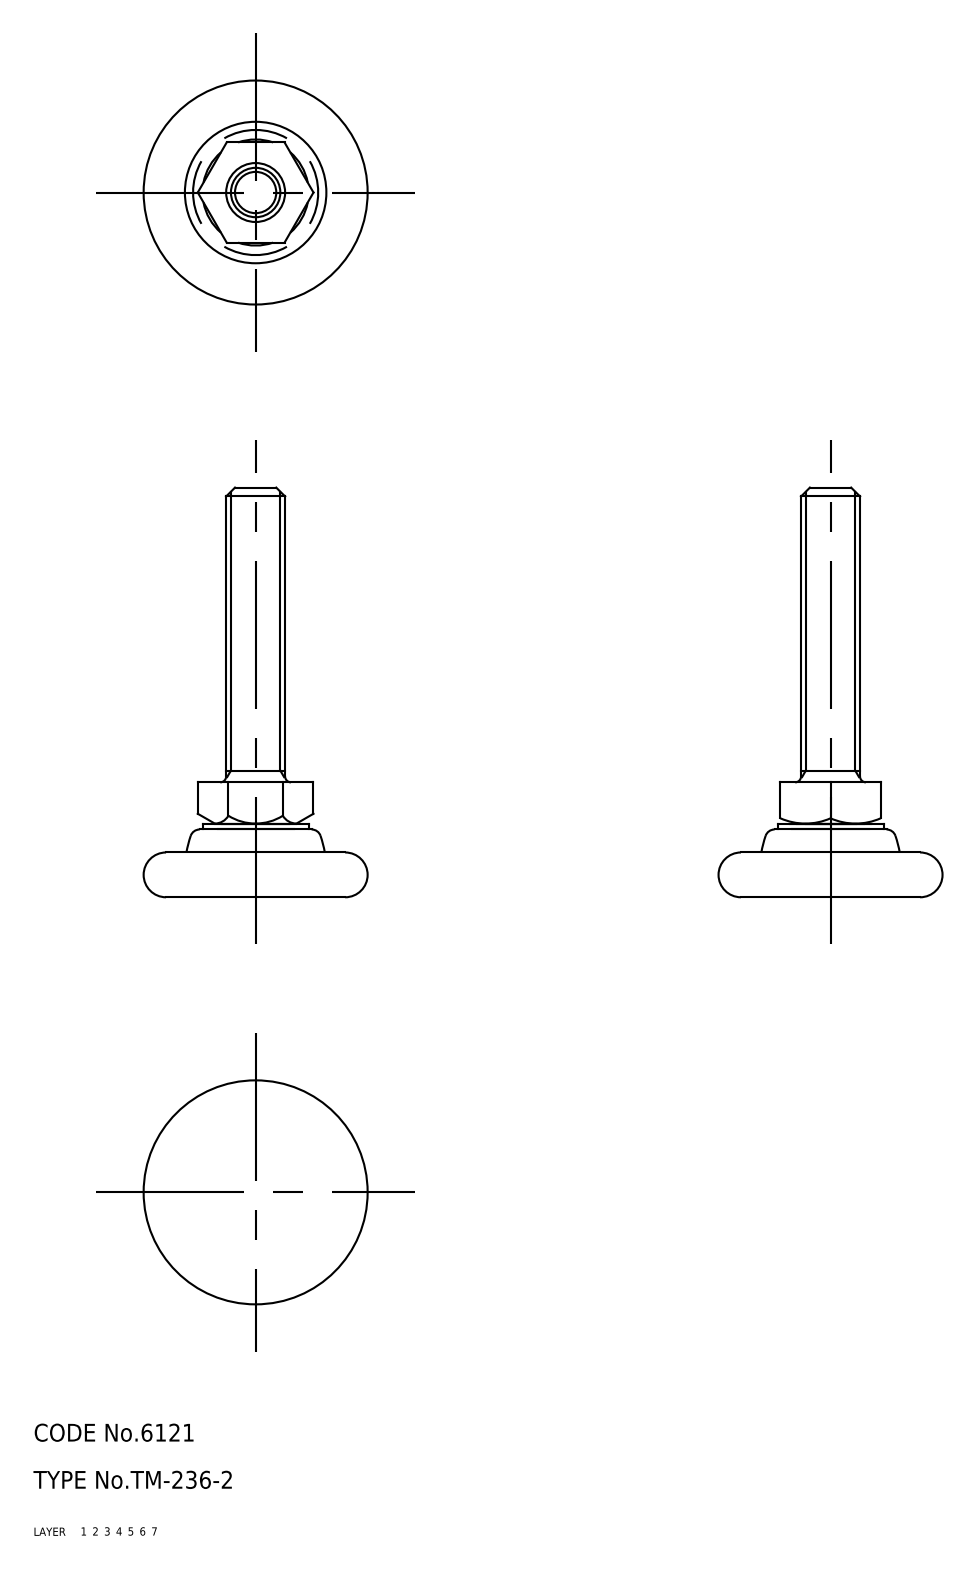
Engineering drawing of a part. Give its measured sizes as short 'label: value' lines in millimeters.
name: washer; rubber pad; foot; bolt (+1 more)
written by: CADfix (AUTOMOTIVE_DESIGN)
unit: mm
bodies: 4 solids, 58 faces (0 planar, 0 cylindrical, 58 other)
size: 69.5 × 38 × 38
volume: 13 227 mm³; area: 8 684 mm²
